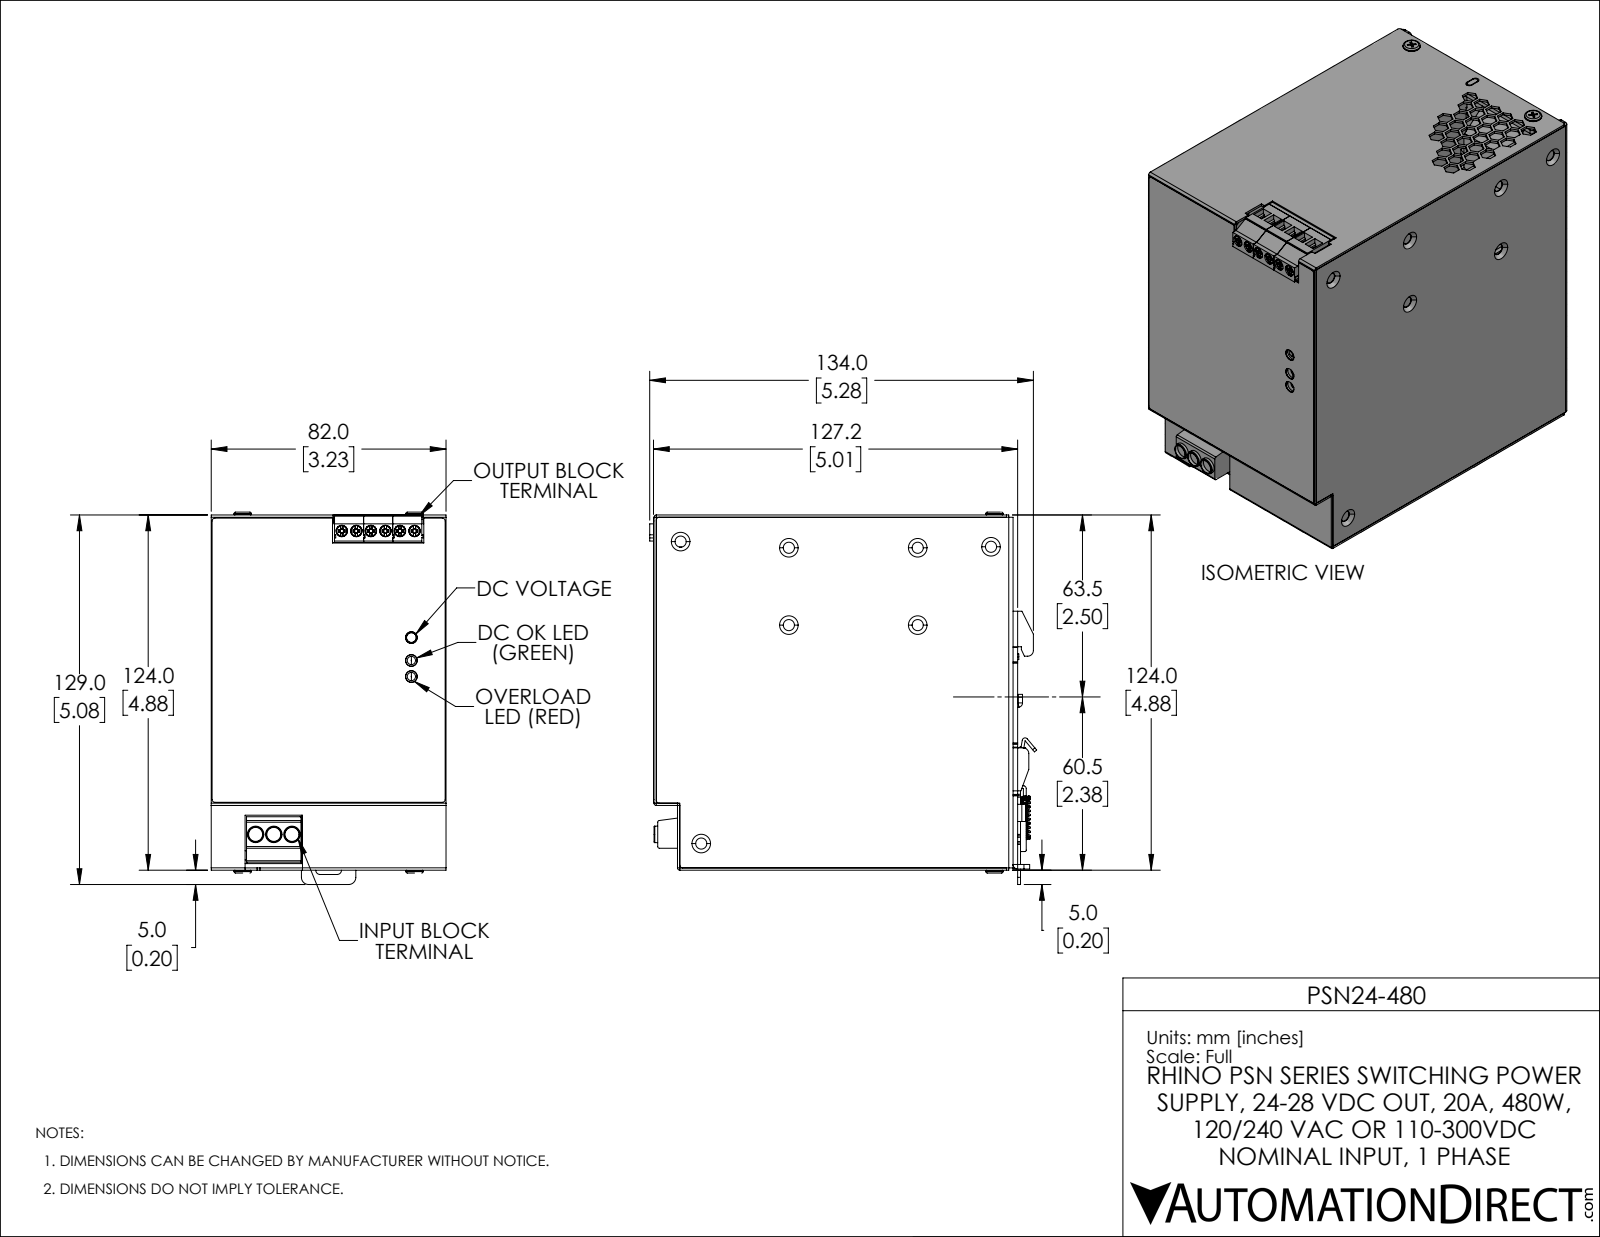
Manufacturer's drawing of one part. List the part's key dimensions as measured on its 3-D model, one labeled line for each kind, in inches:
Part name (STEP PRODUCT): PSN24-480
STEP written by: SolidWorks 2019 (AUTOMOTIVE_DESIGN)
Units: inches
Bodies: 26 solids, 2160 faces (1574 planar, 430 cylindrical, 156 other)
Overall size (bounding box): 5.321 × 5.118 × 3.228
Volume: 6.307 in³ · Surface area: 271.3 in²
Round holes (diameter × count): ⌀0.154 ×18, ⌀0.157 ×9, ⌀0.098 ×8, ⌀0.138 ×3, ⌀0.161 ×3, ⌀0.193 ×3, ⌀0.039 ×2, ⌀0.118 ×2, ⌀0.146 ×1, ⌀0.165 ×1
Round bosses / shafts (diameter × count): ⌀0.217 ×6, ⌀0.154 ×6, ⌀0.227 ×3, ⌀0.236 ×2, ⌀0.114 ×2, ⌀0.079 ×2, ⌀0.134 ×1
Partial cylindrical surfaces — rounded edges, fillets, slot ends (radius × count): R0.01 ×60, R0.039 ×43, R0.02 ×41, R0.004 ×16, R0.012 ×16, R0.008 ×8, R0.059 ×7, R0.063 ×6
Main face-to-face distances: 0.059, 3.169, 0.031, 4.85, 3.228, 3.11, 4.937, 4.819, 4.878, 4.882
Hole centre spacings: 0.2, 0.4, 0.787, 3.075, 3.213, 0.6, 2.643, 0.25
